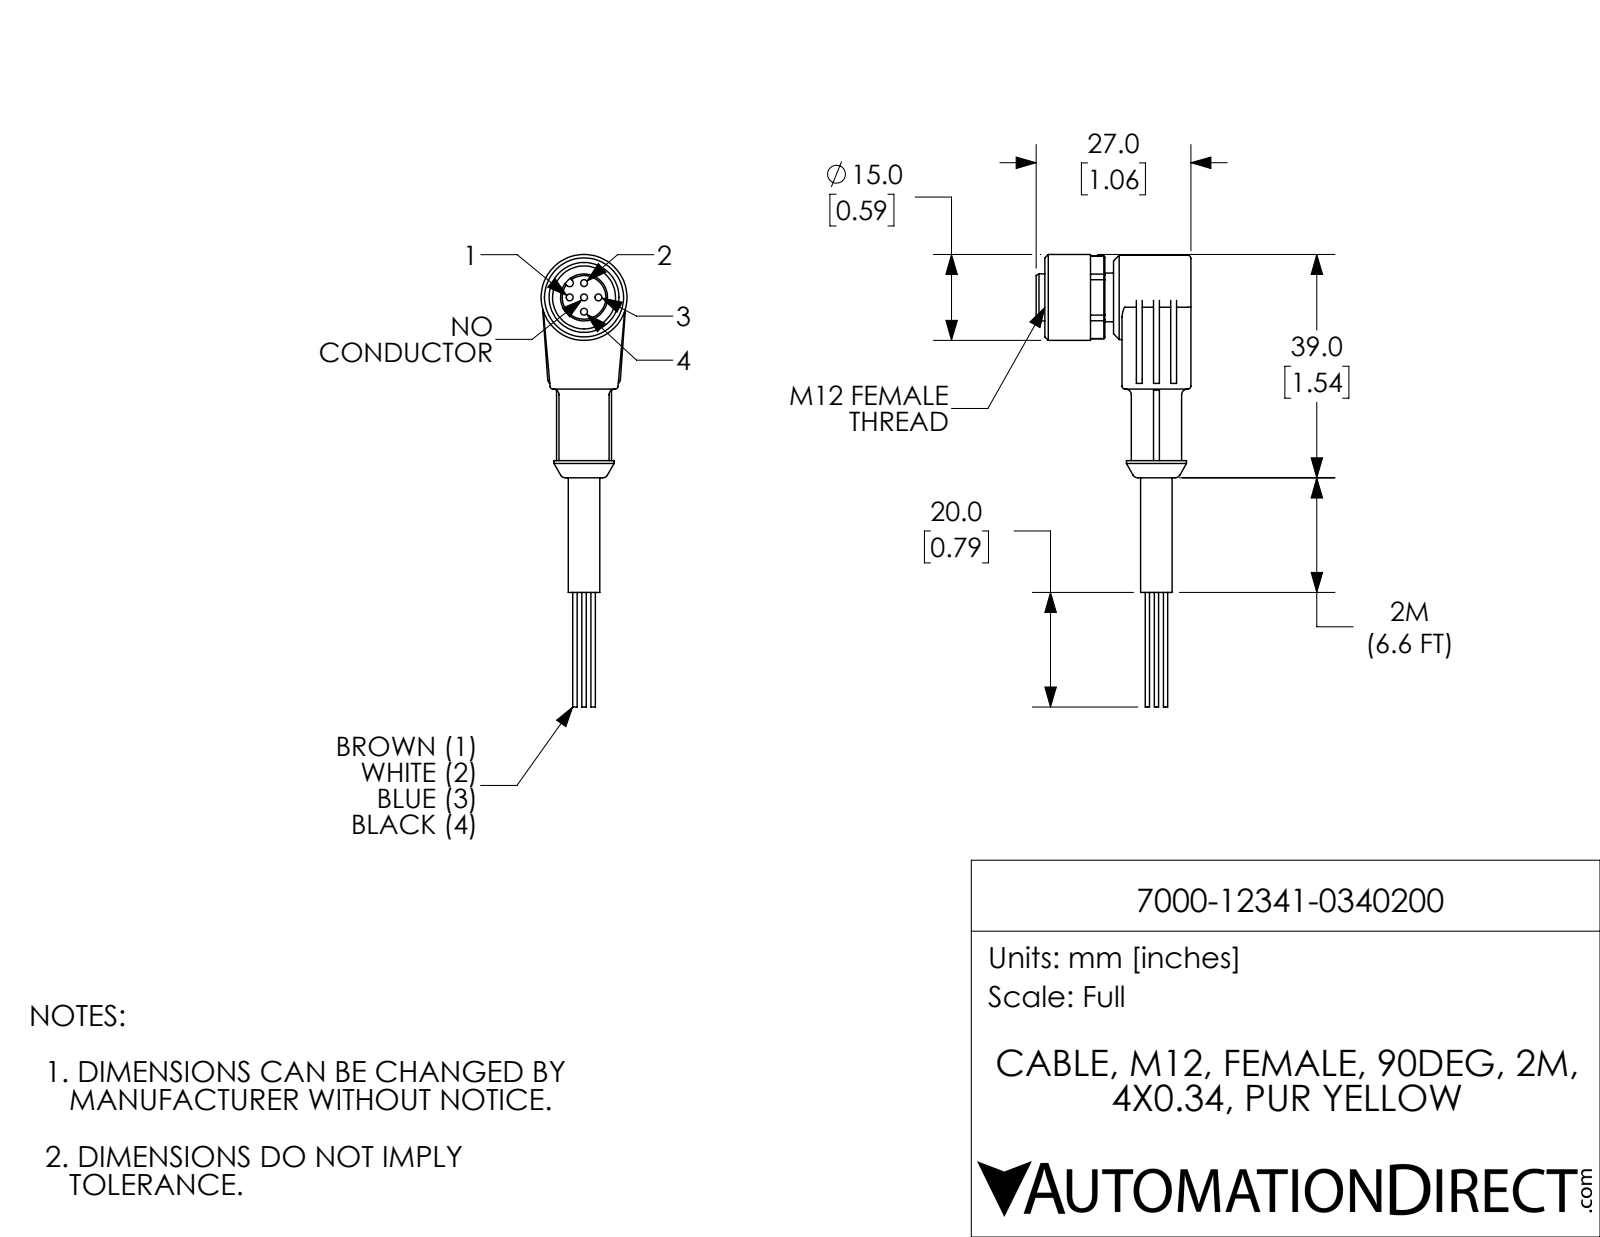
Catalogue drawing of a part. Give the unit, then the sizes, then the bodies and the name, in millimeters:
Units: millimetres
Overall size (bounding box): 79 × 27 × 15
Round holes (diameter × count): ⌀1.2 ×5, ⌀4.8 ×1, ⌀11 ×1
Round bosses / shafts (diameter × count): ⌀0.8 ×4, ⌀15 ×1, ⌀14.7 ×1, ⌀10.5 ×1, ⌀8.8 ×1, ⌀8.5 ×1, ⌀8.2 ×1, ⌀5.5 ×1
Partial cylindrical surfaces — rounded edges, fillets, slot ends (radius × count): R0.5 ×8, R1 ×2, R0.7 ×1, R7.2 ×1
Main face-to-face distances: 12, 1.5, 3, 13.5, 15, 5.5, 9.5, 6, 8, 12.5
Hole centre spacings: 2.5, 3.5, 5
Volume: 6 830 mm³ · Surface area: 3 804 mm²
Bodies: 1 solid, 152 faces (65 planar, 59 cylindrical, 28 other)
Part name (STEP PRODUCT): 7000-12341-0340200
STEP written by: SolidWorks 2021 (CONFIG_CONTROL_DESIGN)
